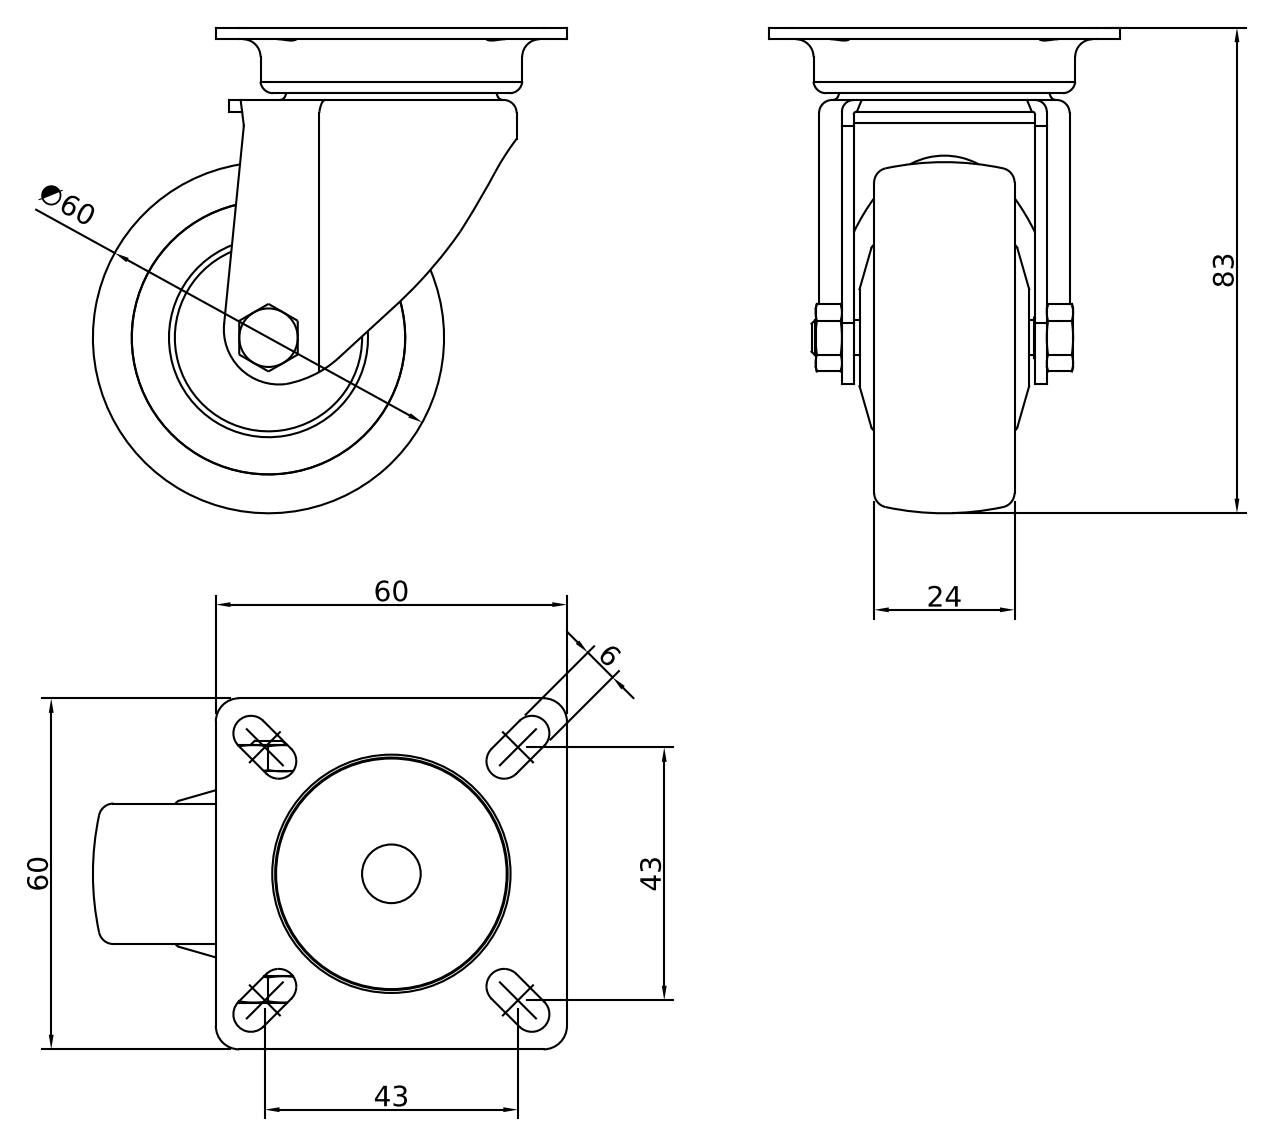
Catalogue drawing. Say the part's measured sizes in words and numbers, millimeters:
The part is named "CRUST0000178; 440000025269; 440000025270; 440000025272 (+3 more)". Its 3-D file was written by "Autodesk Inventor 2022 (AUTOMOTIVE_DESIGN)". It is 7 solids with 188 faces: 69 planar, 55 cylindrical and 64 other. Overall it measures 83 by 81 by 60 millimeters. Its volume is 84 714 cubic millimeters and its surface area 39 404 square millimeters. Round holes: 1 of diameter 4.92, 1 of diameter 6, 1 of diameter 8, 1 of diameter 10.02, 1 of diameter 31, 1 of diameter 34, 1 of diameter 34, 1 of diameter 40.72, 1 of diameter 46.74. Round bosses or shafts: 1 of diameter 46.7, 1 of diameter 44.72, 1 of diameter 39.72, 1 of diameter 32, 1 of diameter 31.72, 1 of diameter 7.9, 1 of diameter 5.9. Partial cylindrical surfaces (rounded edges, fillets, slot ends): 8 of radius 3, 4 of radius 4, 2 of radius 0.5, 2 of radius 2, 1 of radius 9.42, 1 of radius 18.1, 1 of radius 19.4, 1 of radius 21.4. The main face-to-face distances are 2, 29.5, 3.5, 24, 5.5, 12.38, 27.5, 33, 10, 10.38.
